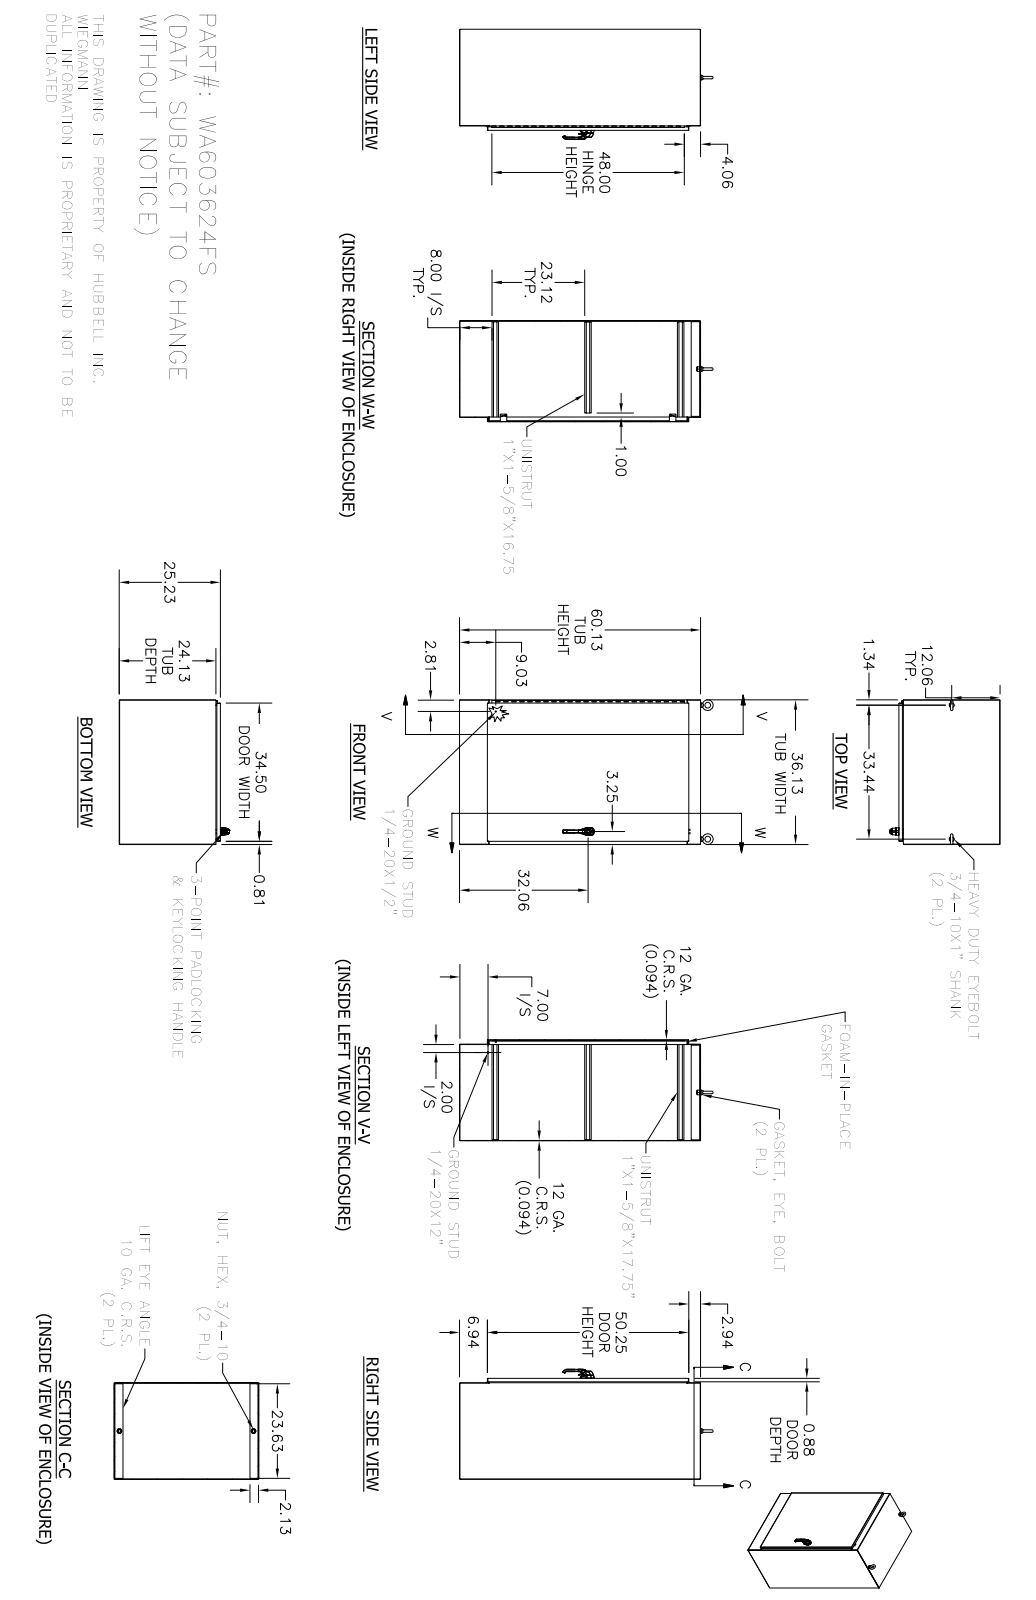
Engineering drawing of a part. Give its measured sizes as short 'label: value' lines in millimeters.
name: WA603624FSBLS; WA6024FSRS; WA3624FSTOP; WA3624FSBTM (+8 more)
written by: Autodesk Inventor 2014 (AUTOMOTIVE_DESIGN)
unit: mm
bodies: 46 solids, 2641 faces (1072 planar, 922 cylindrical, 647 other)
size: 1606.49 × 917.58 × 697.88
volume: 16 000 000 mm³; area: 13 300 000 mm²
holes: 8× ⌀7.02, 8× ⌀9.52, 4× ⌀5.08, 3× ⌀5.4, 3× ⌀7.11, 2× ⌀8, 2× ⌀10.2, 2× ⌀10.33, 2× ⌀10.5, 2× ⌀16.31, 2× ⌀20.64, 1× ⌀3.1
bosses: 2× ⌀31.75, 2× ⌀28.45, 2× ⌀19.05, 2× ⌀13.5, 2× ⌀13.37, 2× ⌀11.05, 2× ⌀8.56, 2× ⌀6.35
rounds: 170× R0.5, 100× R0.3, 21× R0.47, 16× R0.25, 16× R3.17, 15× R0.79, 14× R2, 13× R3.17
face distances: 2.38, 638.38, 915.2, 1524.8, 636, 640.76, 912.82, 917.58, 610.4, 27.98
hole spacings: 135.47, 406.4, 270.93, 541.87, 1081.3, 9.66, 9.7, 9.71
